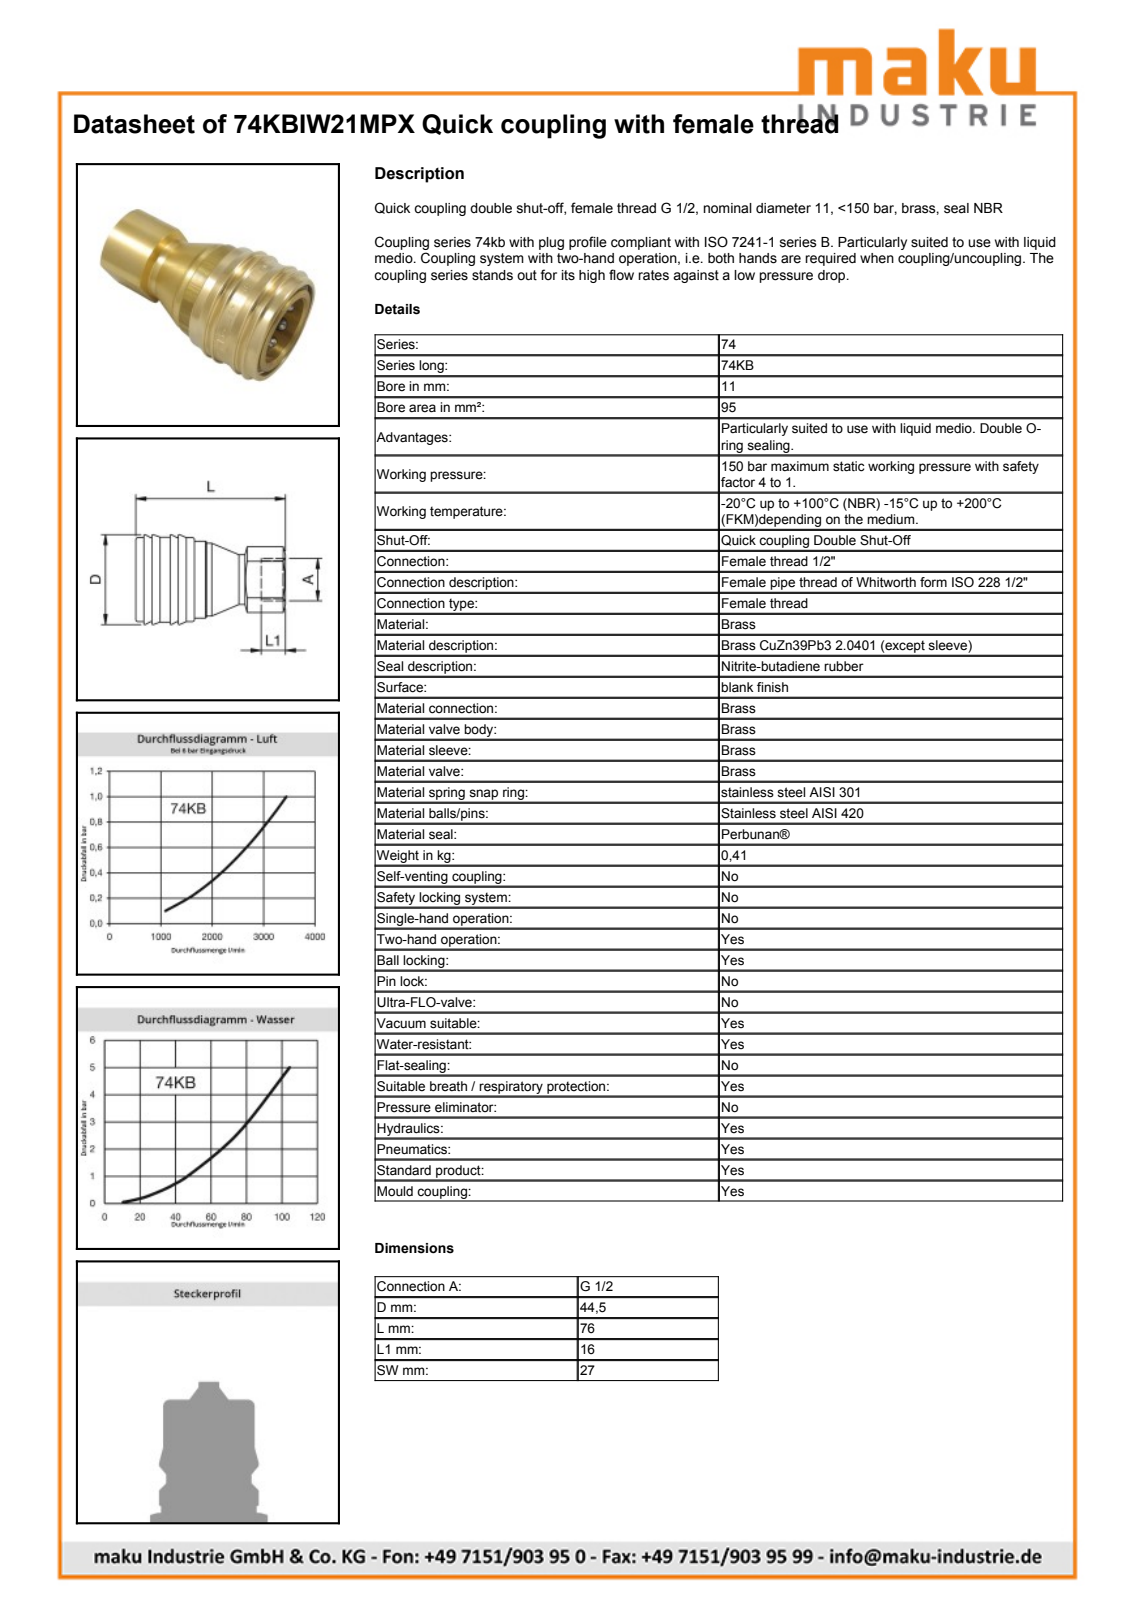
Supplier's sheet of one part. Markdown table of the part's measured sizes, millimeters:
| quantity | value |
| --- | --- |
| part name | D107742 |
| STEP written by | Autodesk Inventor 2013 (AUTOMOTIVE_DESIGN) |
| units | millimeters |
| bodies | 1 solid, 703 faces (304 planar, 75 cylindrical, 324 other) |
| overall size | 76 × 44.5 × 44.5 |
| volume | 69 165 mm³ |
| surface area | 20 049 mm² |
| round holes (diameter × count) | 18.63 × 1, 33.55 × 1, 37.2 × 1, 38.2 × 1 |
| round bosses / shafts (diameter × count) | 42 × 1, 41.5 × 1, 40.81 × 1, 38 × 1, 37.8 × 1, 36 × 1, 33.25 × 1, 24.6 × 1 |
| partial cylindrical surfaces (radius × count) | 16.25 × 1, 20.9 × 1 |
| main face-to-face distances | 27, 62.27, 8.8, 53.47, 4, 76, 67.2, 13.73, 23.4, 14.6 |
